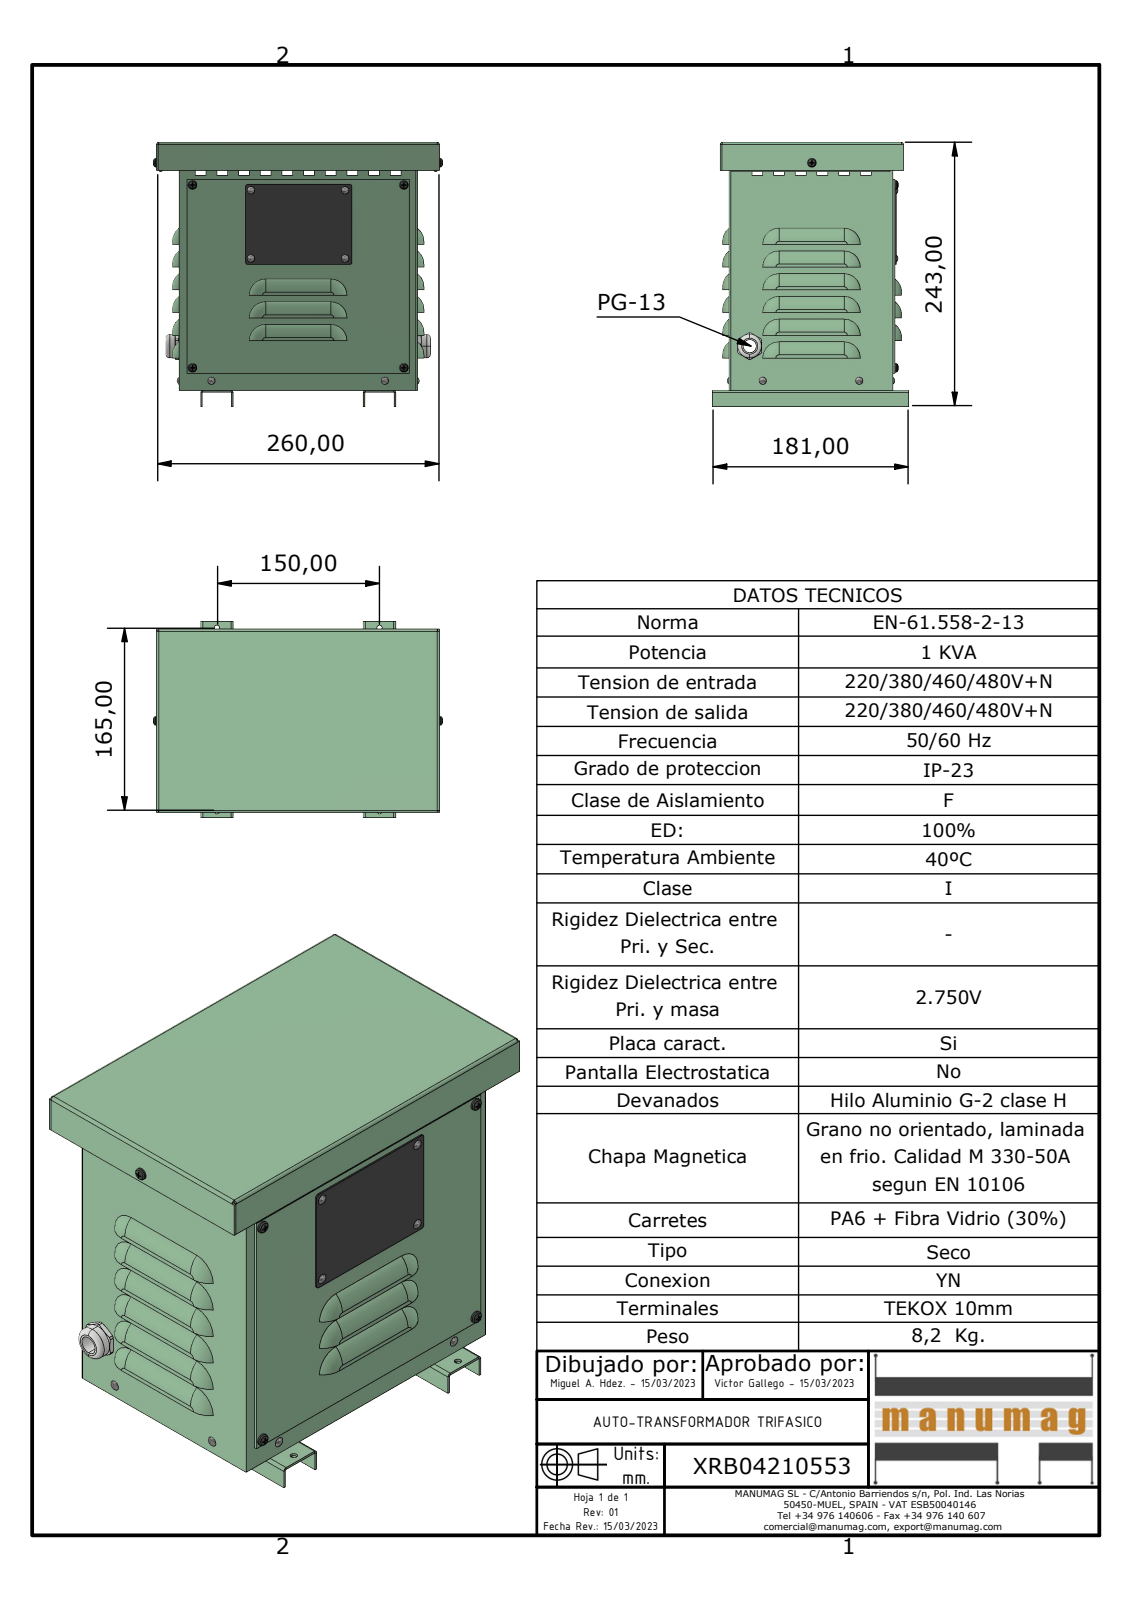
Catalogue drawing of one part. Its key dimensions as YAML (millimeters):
part_name: "XRB04210553; JE001 - JE002 EXPORT CUERPO; JE001 - JE002 EXPORT BASE; JE001 - JE002 EXPORT PATA (+6 more)"
step_written_by: "Autodesk Inventor 2023 (AUTOMOTIVE_DESIGN)"
units: millimeters
bodies: {solids: 27, faces: 1168, planar: 639, cylindrical: 259, other: 270}
overall_size: [267.13, 244.49, 181]
volume: 601317
surface_area: 669713
round_holes:
  - {diameter: 4.8, count: 13}
  - {diameter: 3.8, count: 5}
  - {diameter: 3, count: 4}
  - {diameter: 4, count: 4}
  - {diameter: 12, count: 1}
  - {diameter: 22, count: 1}
round_bosses_or_shafts:
  - {diameter: 3.2, count: 8}
  - {diameter: 4, count: 5}
  - {diameter: 3.62, count: 5}
  - {diameter: 21.7, count: 1}
  - {diameter: 20.4, count: 1}
  - {diameter: 20.3, count: 1}
  - {diameter: 18.95, count: 1}
partial_cylinders:
  - {radius: 14, count: 24}
  - {radius: 15, count: 21}
  - {radius: 4, count: 18}
  - {radius: 1.5, count: 13}
  - {radius: 2, count: 12}
  - {radius: 0.5, count: 8}
  - {radius: 2.5, count: 8}
  - {radius: 14.5, count: 6}
face_to_face_distances: [1.5, 149.5, 227.99, 218.5, 229.49, 151.5, 151, 2, 153, 217]
hole_center_spacings: [169, 150, 21.22, 26, 43.01, 50, 54.23, 63]
